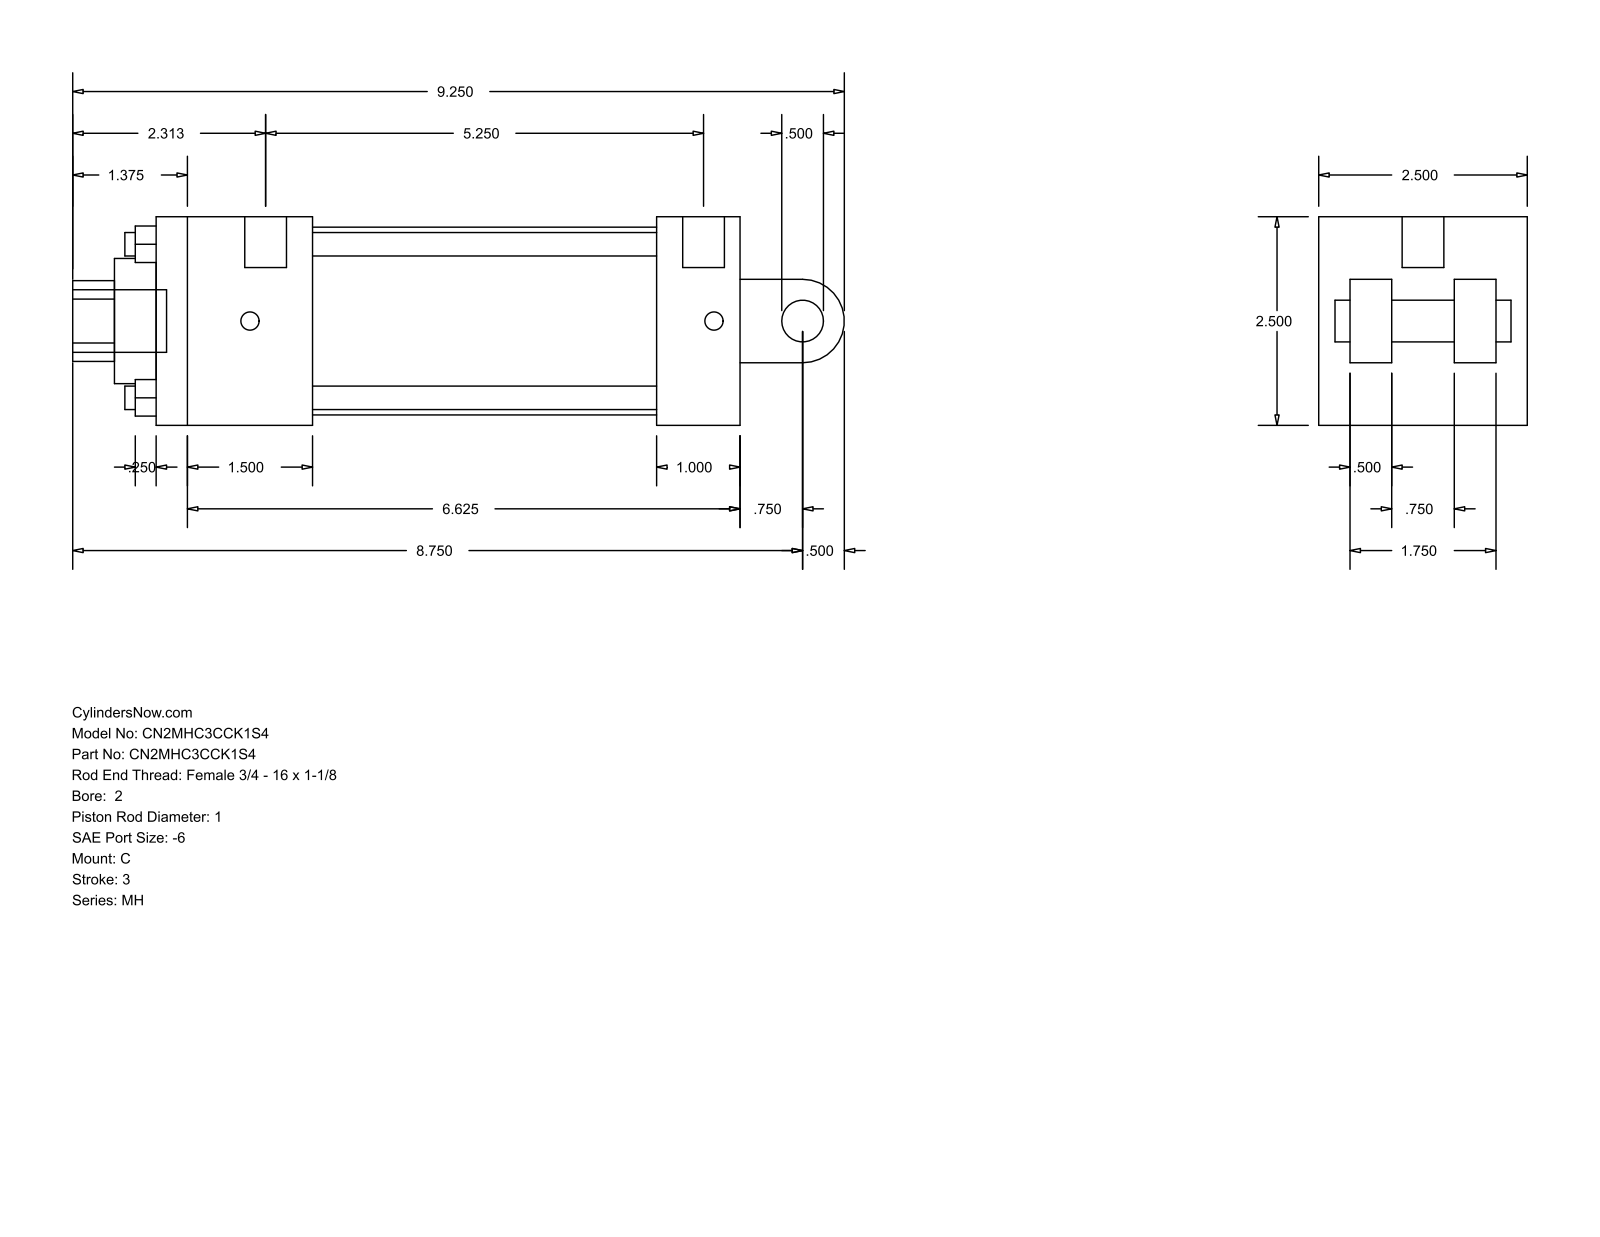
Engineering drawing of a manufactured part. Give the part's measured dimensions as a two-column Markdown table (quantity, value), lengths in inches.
| quantity | value |
| --- | --- |
| part name | MH_C__0200_1 |
| STEP written by | GSSL Pune (CONFIG_CONTROL_DESIGN) |
| units | inches |
| bodies | 0 solids, 99 faces (70 planar, 29 cylindrical, 0 other) |
| overall size | 9.25 × 2.5 × 2.5 |
| round holes (diameter × count) | 0.281 × 4, 0.219 × 2, 0.5 × 1, 1 × 1, 1.5 × 1, 2.25 × 1 |
| round bosses / shafts (diameter × count) | 0.5 × 2, 0.219 × 2, 0.75 × 1 |
| partial cylindrical surfaces (radius × count) | 0.484 × 1, 0.5 × 1 |
| main face-to-face distances | 2.5, 7, 0.5, 1, 0.375, 1.875, 2.125, 6, 4.125, 5.125 |
| hole center spacings | 1.301, 1.84, 2.602, 0.125 |
